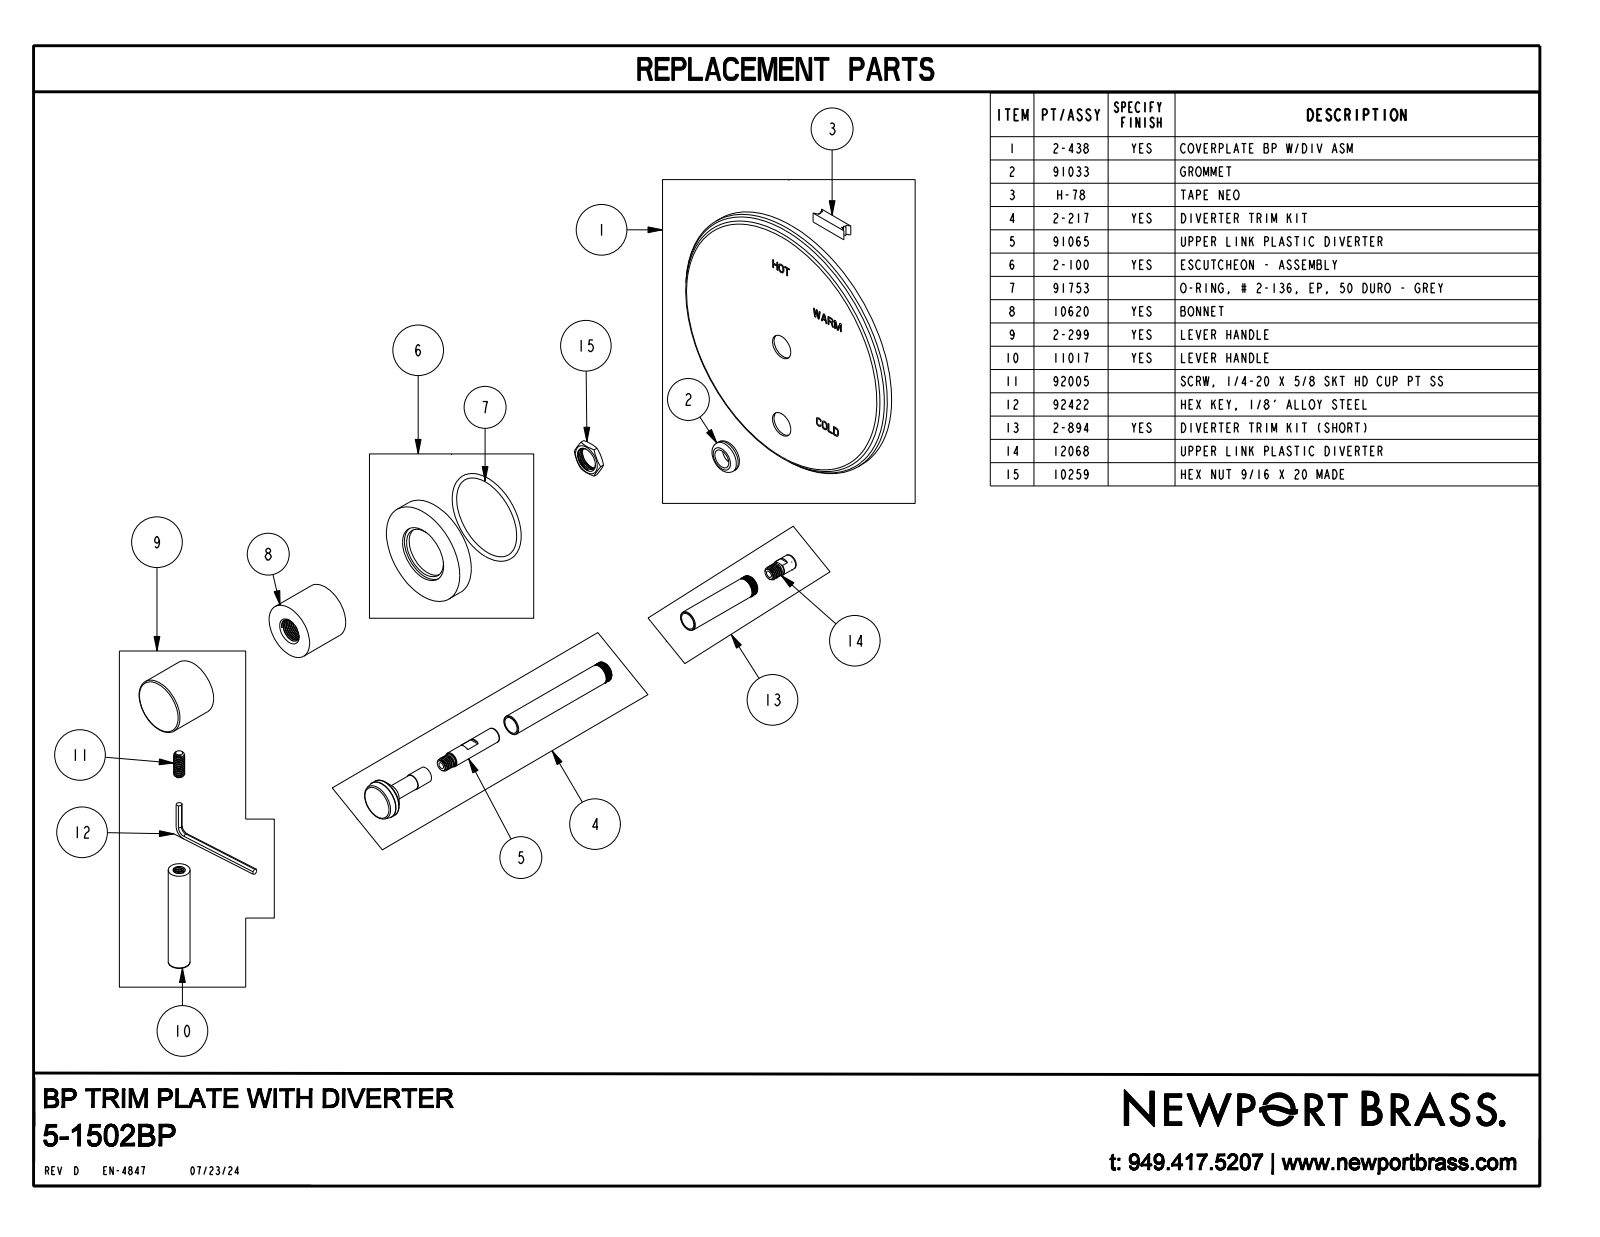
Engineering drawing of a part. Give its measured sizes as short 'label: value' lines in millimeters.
name: 5-1502BP
written by: CREO PARAMETRIC BY PTC INC, 2018400 (CONFIG_CONTROL_DESIGN)
unit: mm
bodies: 1 solid, 315 faces (271 planar, 20 cylindrical, 24 other)
size: 165.1 × 165.1 × 74.6
volume: 257 100 mm³; area: 59 810 mm²
holes: 1× ⌀13.2
bosses: 1× ⌀165.1, 1× ⌀60.3, 1× ⌀33.4, 1× ⌀33.3, 1× ⌀22.9, 1× ⌀12.7, 1× ⌀12, 1× ⌀10.2
face distances: 8, 17.5, 9.5, 74.6, 66.6, 57.1, 45.6, 37.7, 28.1, 29
